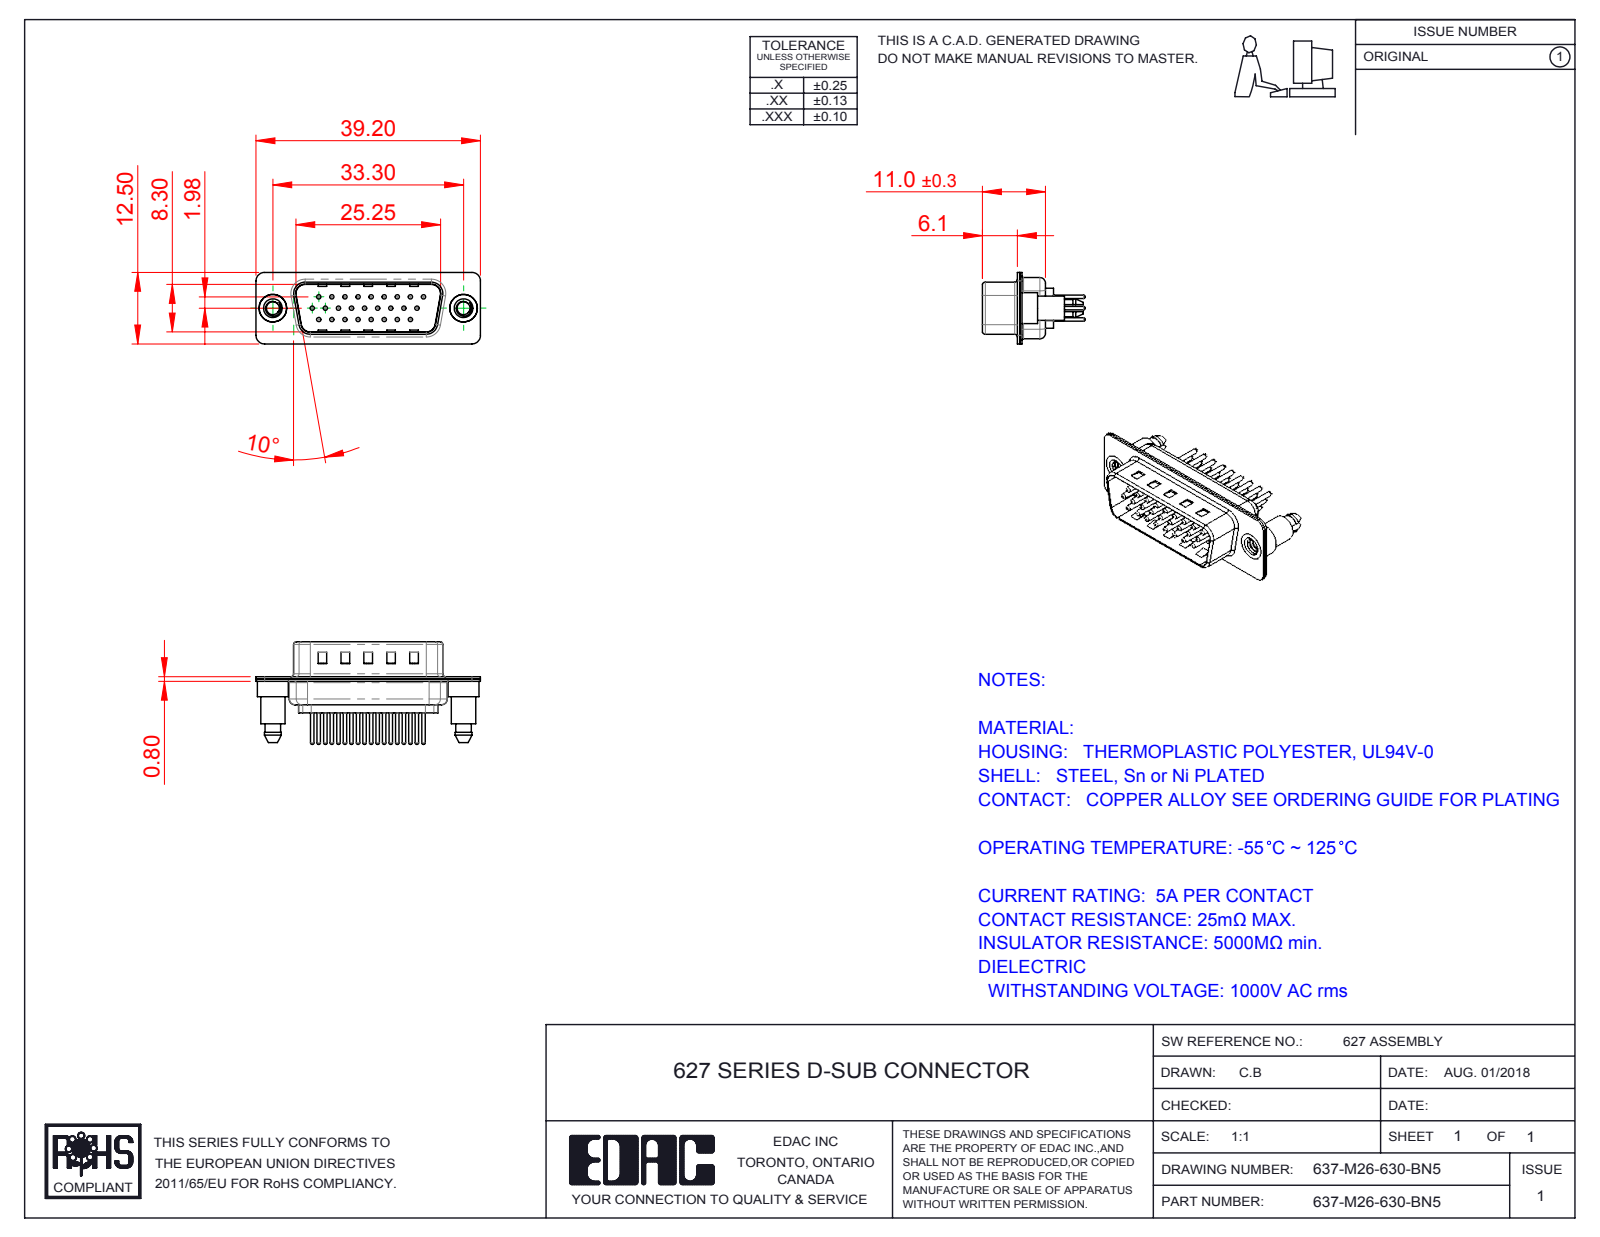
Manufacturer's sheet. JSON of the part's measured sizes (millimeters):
{"part_name": "637M Housing_26 Contacts; 637M Contact Row 3_30; 637-M26-630-BN5; 637M Contact Row 1_30 (+4 more)", "step_written_by": "SolidWorks 2016 (CONFIG_CONTROL_DESIGN)", "units": "millimeters", "bodies": {"solids": 31, "faces": 1352, "planar": 337, "cylindrical": 529, "other": 486}, "overall_size": [39.2, 17.9, 12.5], "volume_mm3": 2043, "surface_area_mm2": 6084, "round_holes": [[0.75, 26], [1.6, 26], [2, 26], [2.26, 2], [4, 2], [4.8, 2]], "round_bosses_or_shafts": [[1.5, 26], [0.6, 26], [5.4, 2], [4.9, 2], [4.25, 2]], "partial_cylinders_radius": [[1.5, 18], [2, 12], [1.6, 10], [0.5, 8], [0.25, 4], [0.6, 4], [0.65, 4], [0.9, 4]], "face_to_face_distances": [0.4, 0.8, 9.5, 9.1, 8.7, 9.9, 6.3, 0.75, 5.5, 0.35], "hole_center_spacings": [3.96, 2.28, 4.57, 6.05, 2.29, 8.24, 6.86, 10.48]}
